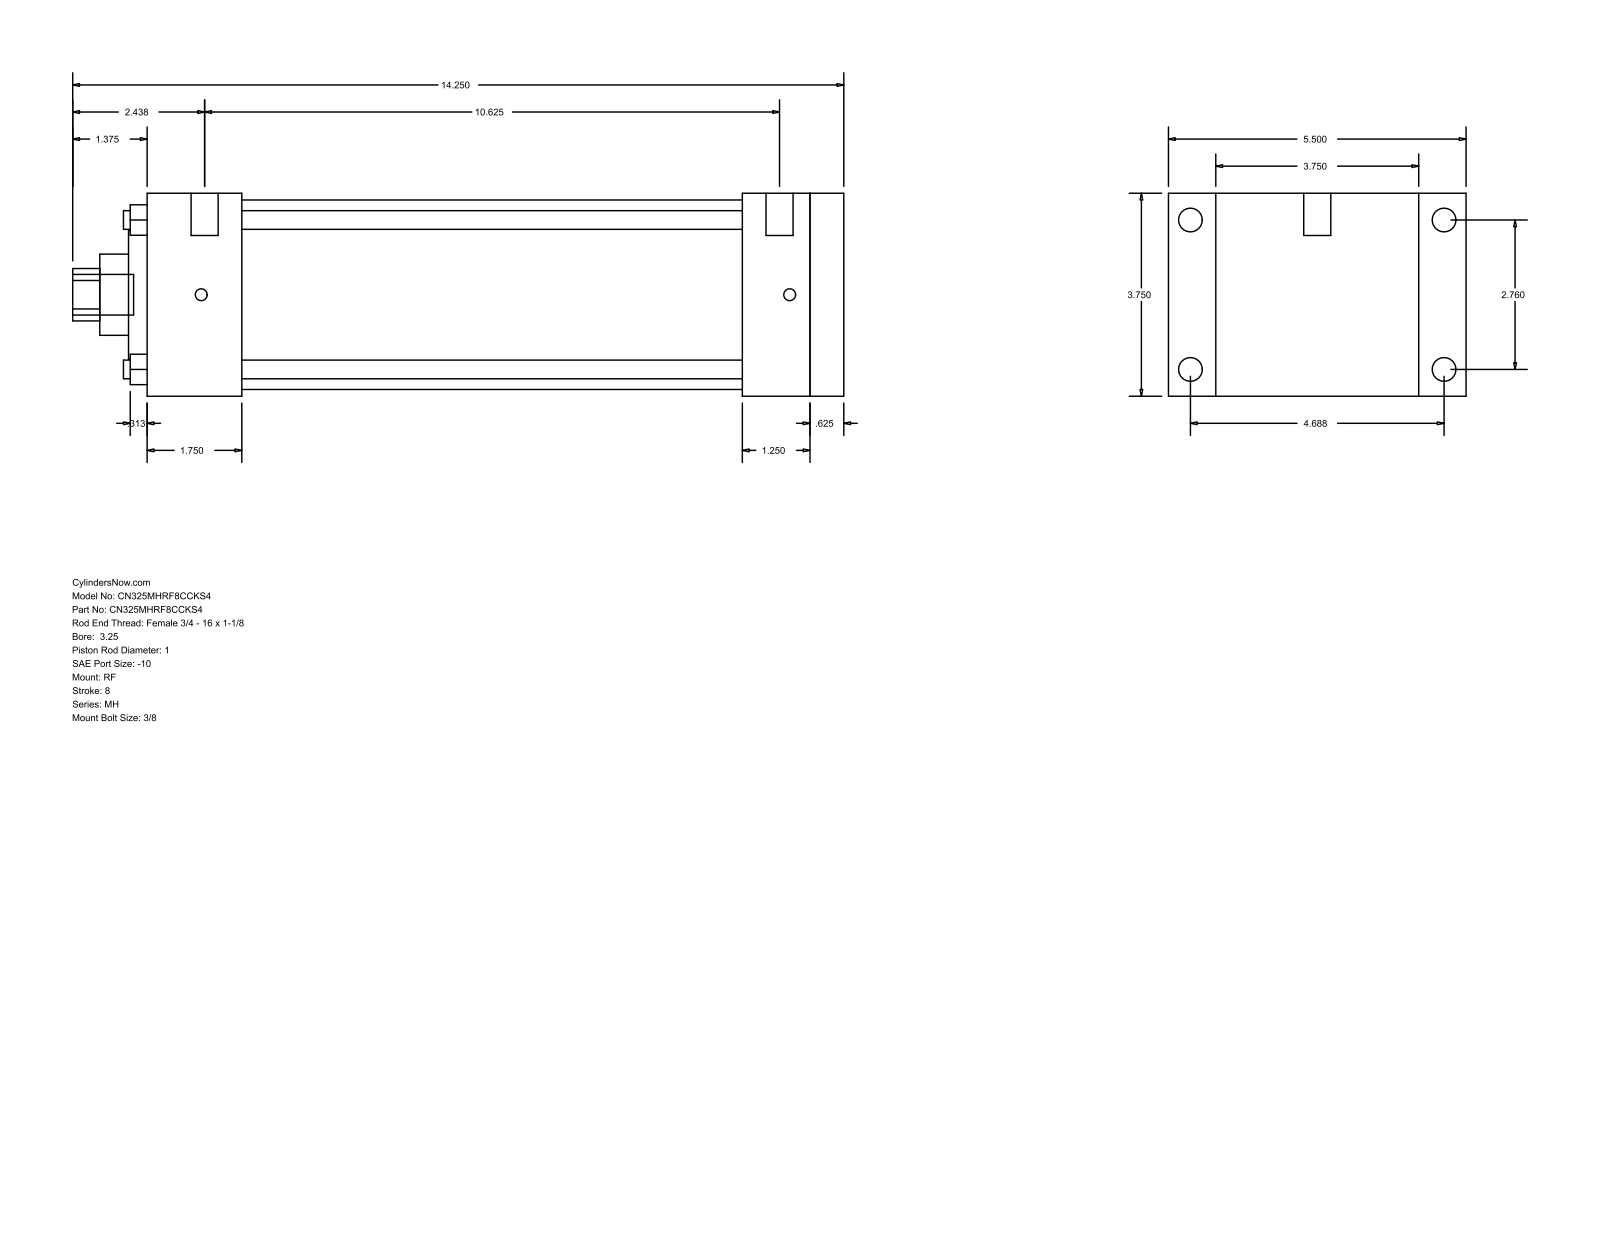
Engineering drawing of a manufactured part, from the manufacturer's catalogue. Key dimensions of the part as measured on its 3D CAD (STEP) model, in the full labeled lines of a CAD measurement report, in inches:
Part name (STEP PRODUCT): MH_RF__0325_1
STEP written by: GSSL Pune (CONFIG_CONTROL_DESIGN)
Units: inches
Bodies: 0 solids, 94 faces (65 planar, 29 cylindrical, 0 other)
Overall size (bounding box): 14.25 × 5.5 × 3.75
Round holes (diameter × count): ⌀0.345 ×4, ⌀1 ×1, ⌀1.5 ×1, ⌀2.375 ×1, ⌀3.5 ×1
Round bosses / shafts (diameter × count): ⌀0.438 ×4, ⌀0.219 ×4, ⌀0.5 ×2, ⌀0.75 ×1
Partial cylindrical surfaces — rounded edges, fillets, slot ends (radius × count): R0.484 ×1
Main face-to-face distances: 3.75, 12.875, 12.25, 0.625, 0.875, 4.625, 1.75, 10.5, 11.125, 11
Hole centre spacings: 1.952, 2.76, 3.903
